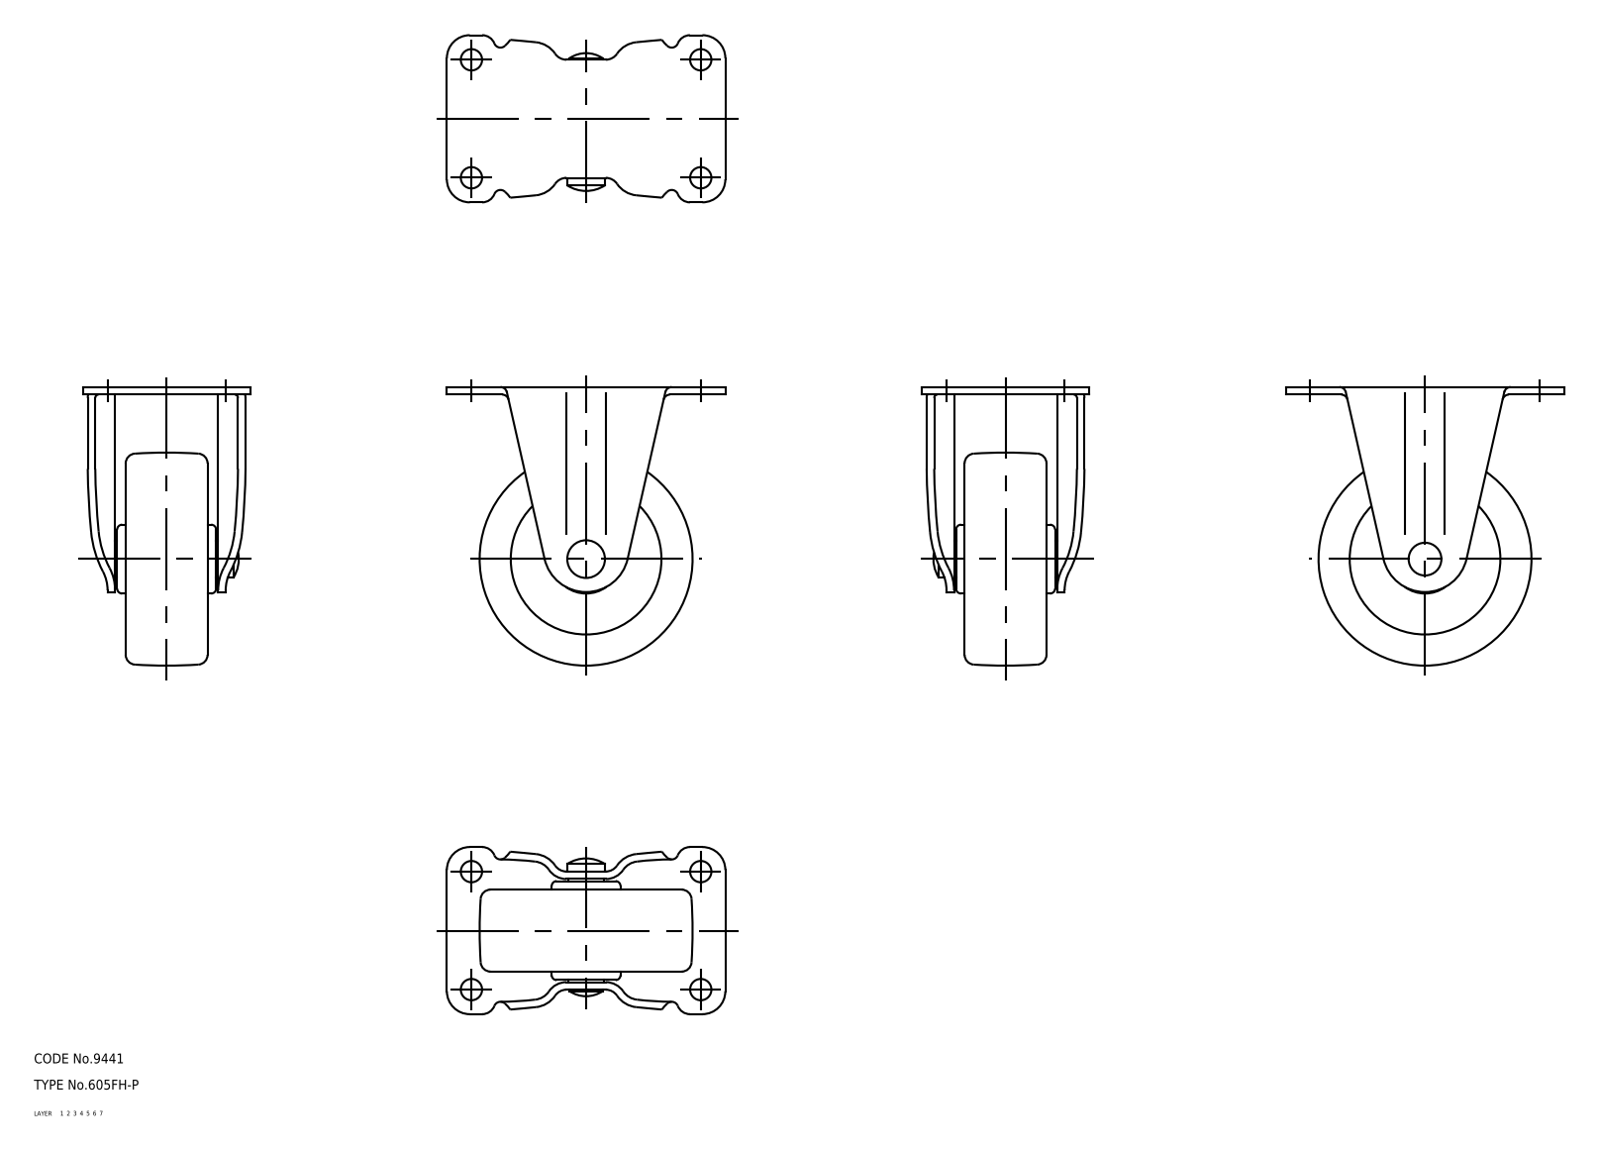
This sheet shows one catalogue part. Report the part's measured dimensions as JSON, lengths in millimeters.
{"part_name": "wheel; axle; No_605FH_P_15361_36", "step_written_by": "CADfix (AUTOMOTIVE_DESIGN)", "units": "millimeters", "bodies": {"solids": 3, "faces": 172, "planar": 0, "cylindrical": 0, "other": 172}, "overall_size": [85, 85, 51], "volume_mm3": 89100, "surface_area_mm2": 32069}
